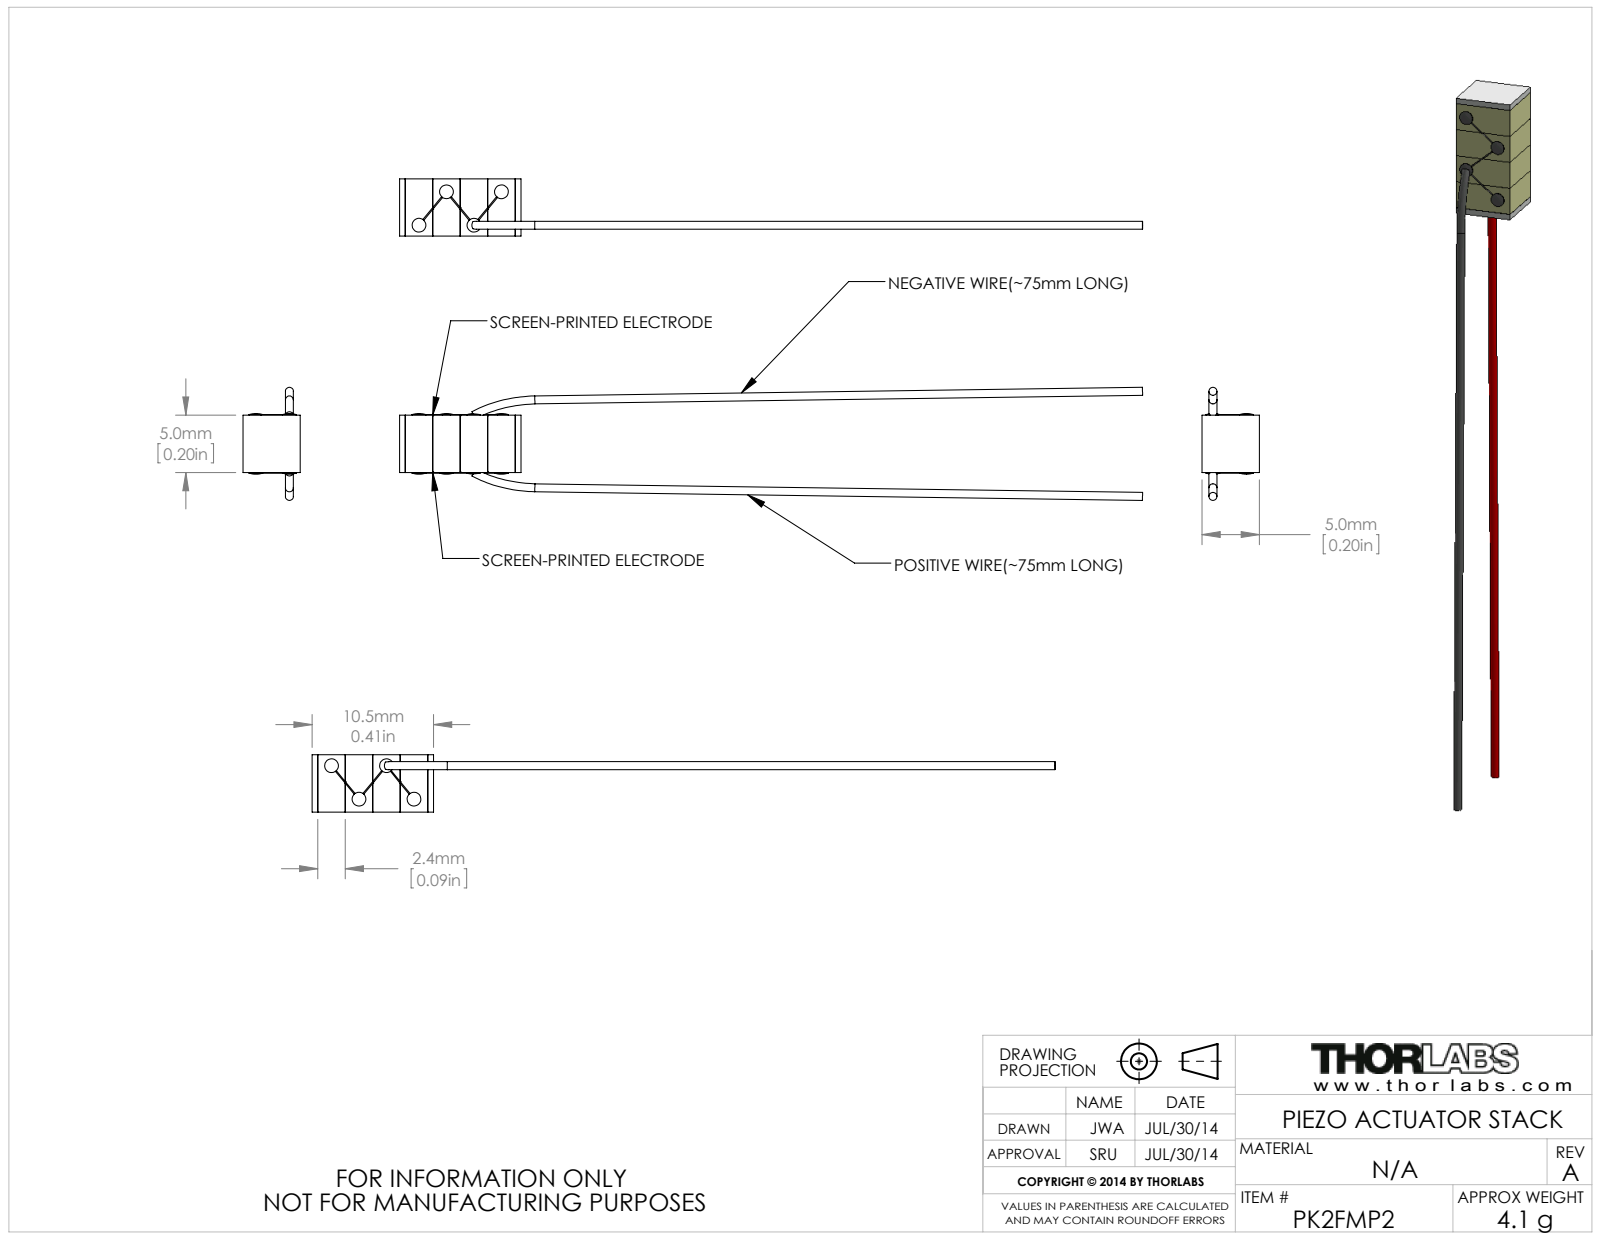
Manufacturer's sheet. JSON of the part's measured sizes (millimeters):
{"part_name": "PK2FMP2", "step_written_by": "SolidWorks 2012 (AUTOMOTIVE_DESIGN)", "units": "millimeters", "bodies": {"solids": 3, "faces": 108, "planar": 44, "cylindrical": 42, "other": 22}, "overall_size": [64.88, 9.87, 5], "volume_mm3": 311, "surface_area_mm2": 771, "round_bosses_or_shafts": [[1.2, 4], [0.7, 2]], "face_to_face_distances": [2.4, 4.8, 5, 7.2, 0.5, 10.11, 2.91, 5.31, 7.71, 2.41]}
